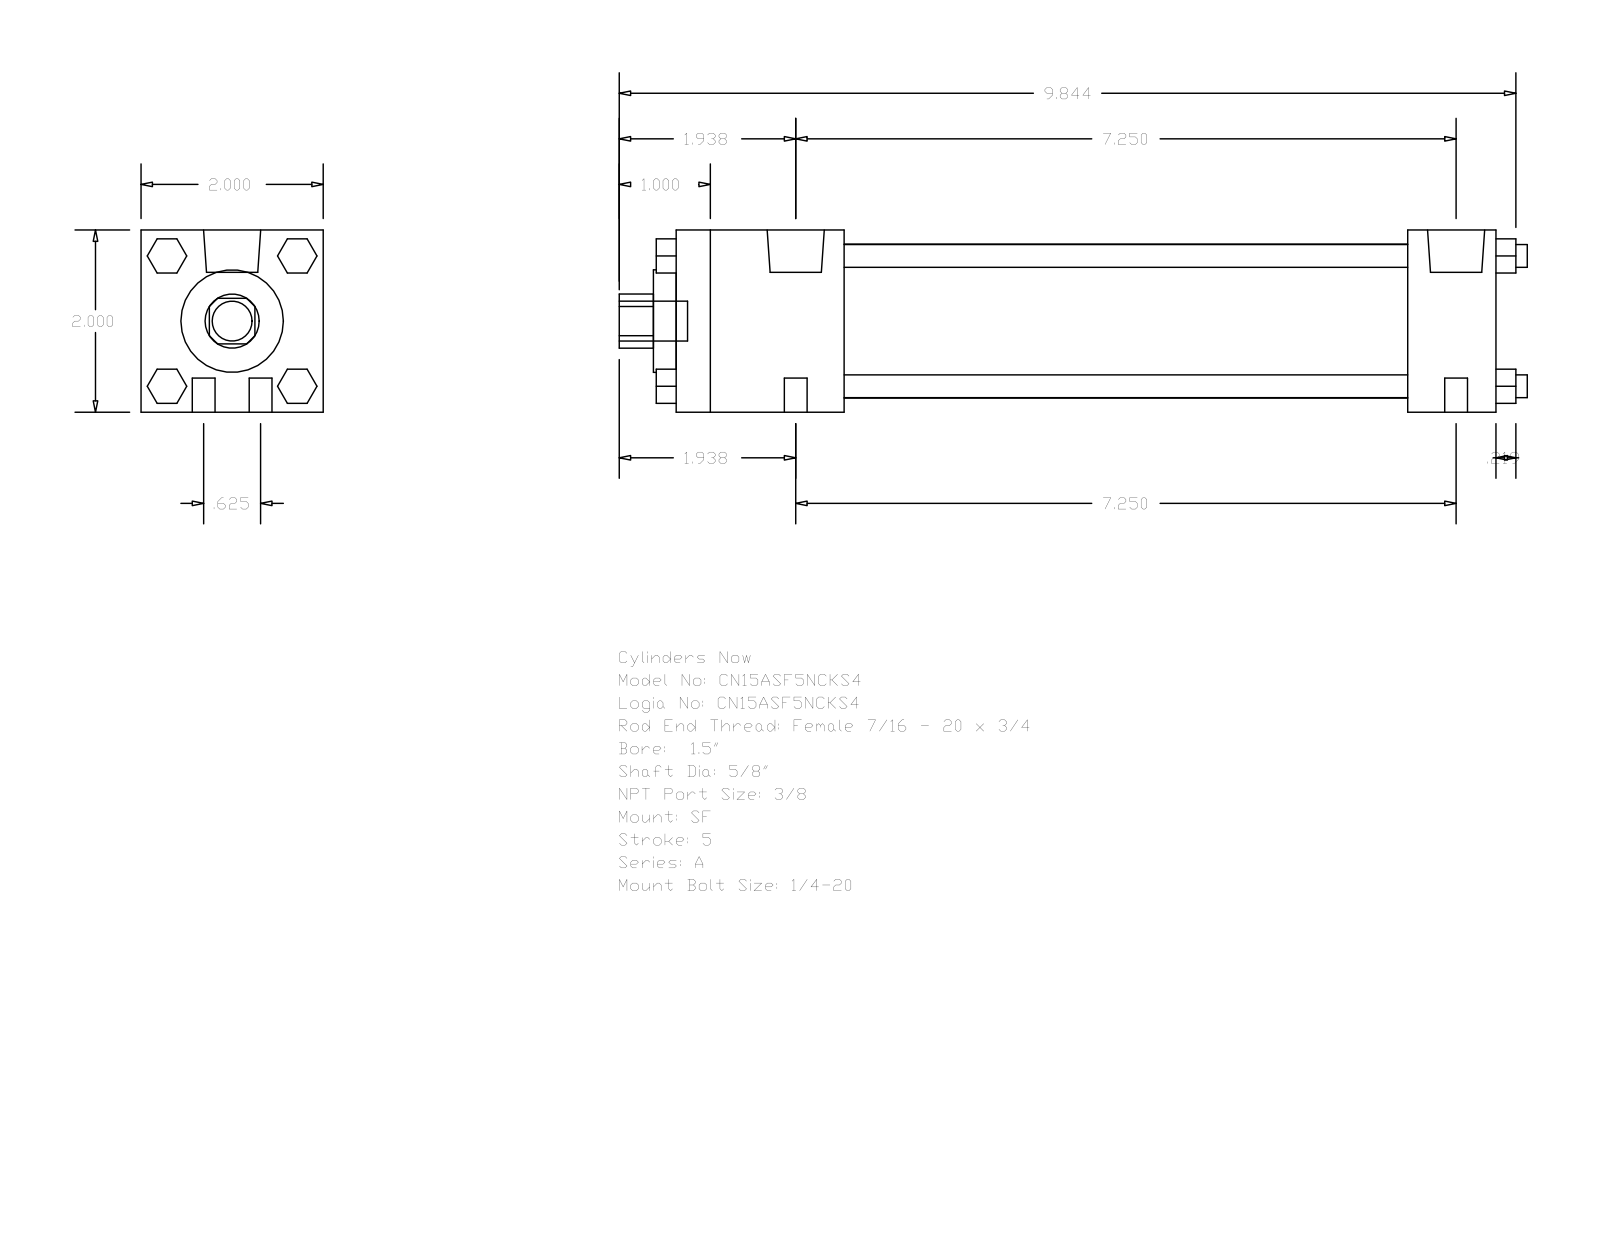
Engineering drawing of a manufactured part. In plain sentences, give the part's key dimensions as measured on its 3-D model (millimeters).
The part is named "A_SF__0150_0.625". Its 3-D file was written by "GSSL Pune (CONFIG_CONTROL_DESIGN)". It is 0 solids with 124 faces: 94 planar, 30 cylindrical and 0 other. Overall it measures 253.21 by 50.8 by 50.8 millimeters. Round holes: 1 of diameter 15.88, 1 of diameter 28.57, 1 of diameter 42.93. Round bosses or shafts: 8 of diameter 6.35, 2 of diameter 15.93, 2 of diameter 5.56, 1 of diameter 11.11. Partial cylindrical surfaces (rounded edges, fillets, slot ends): 1 of radius 7.54. The main face-to-face distances are 50.8, 228.59, 46.83, 203.99, 157.16, 181.76, 24.6, 9.52, 6.35, 53.18.
